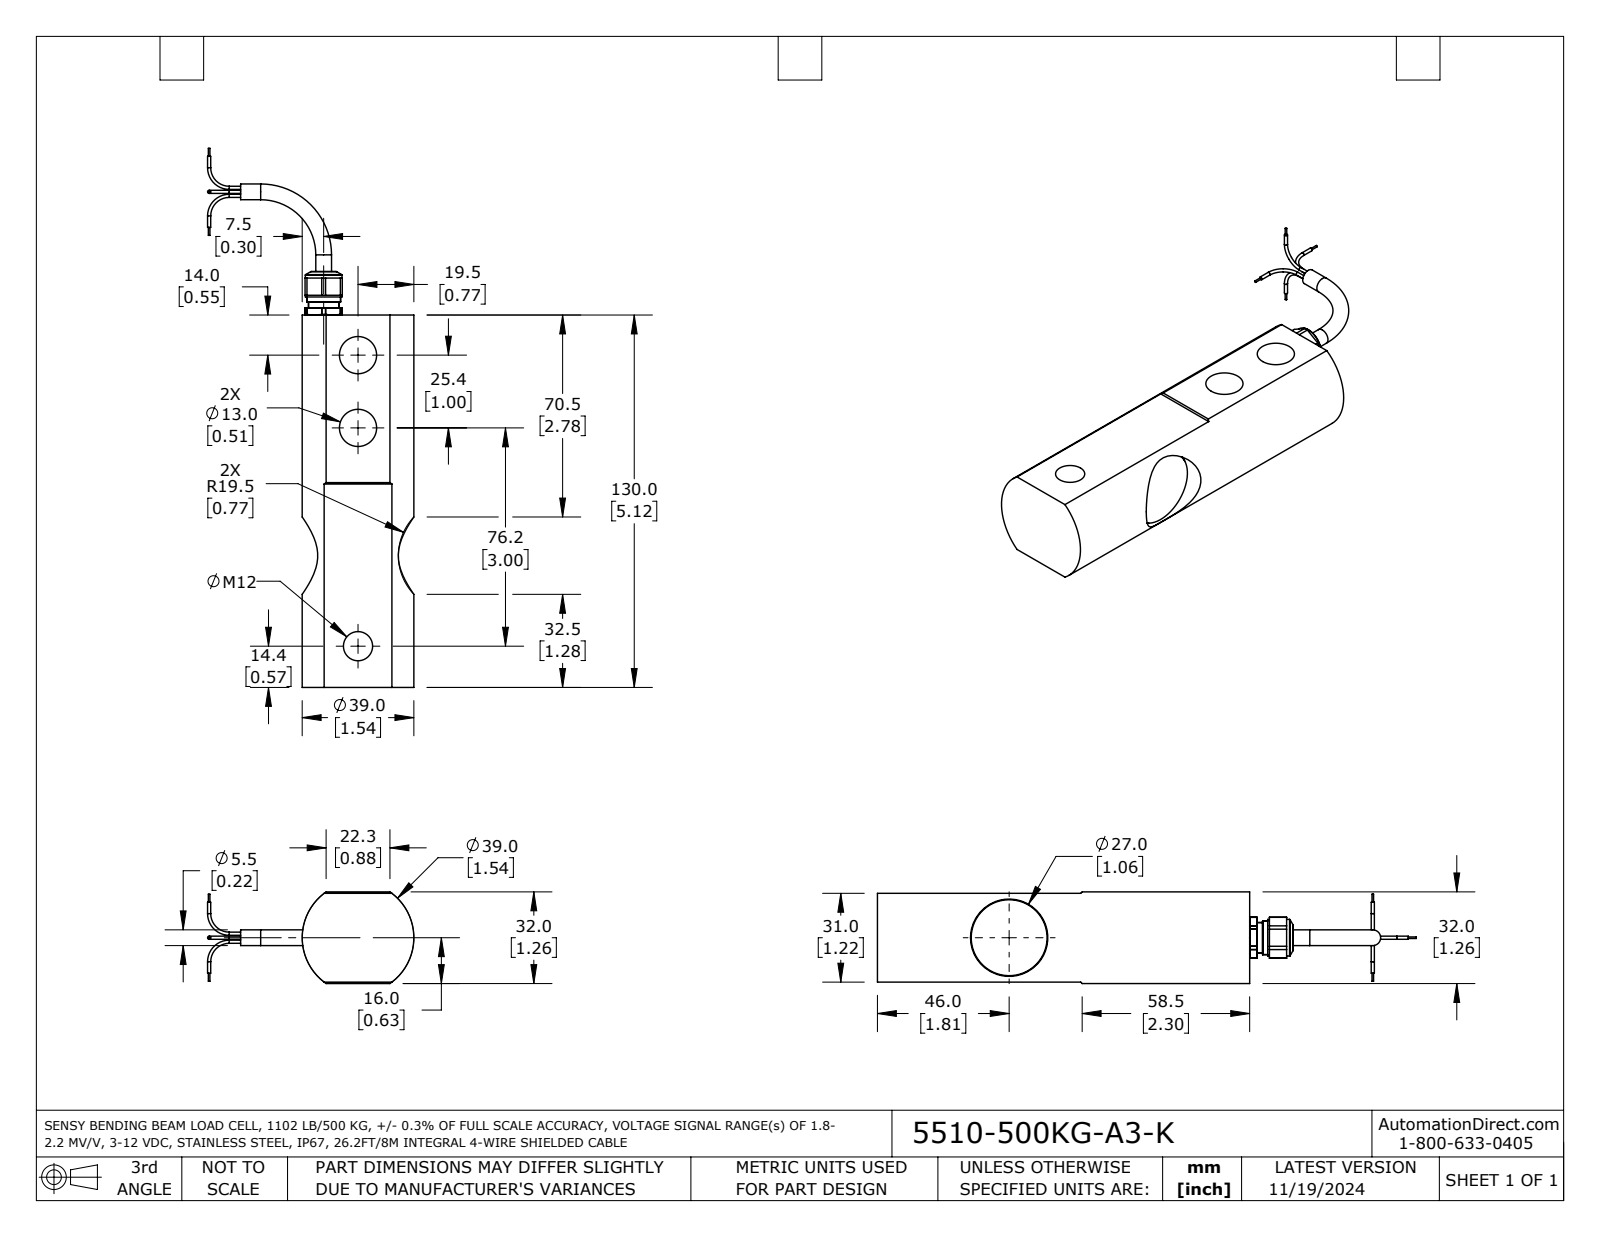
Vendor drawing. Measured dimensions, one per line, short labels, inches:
name: 5510-500KG-A3-K
written by: SolidWorks 2021 (AUTOMOTIVE_DESIGN)
unit: in
bodies: 11 solids, 247 faces (67 planar, 112 cylindrical, 68 other)
size: 7.409 × 2.837 × 1.26
volume: 7.667 in³; area: 42.32 in²
holes: 2× ⌀0.512, 1× ⌀0.126, 1× ⌀0.157, 1× ⌀0.173, 1× ⌀0.24, 1× ⌀0.244, 1× ⌀0.329, 1× ⌀0.354, 1× ⌀0.402, 1× ⌀0.439, 1× ⌀1.063
bosses: 6× ⌀0.043, 2× ⌀0.217, 2× ⌀0.022, 1× ⌀1.043, 1× ⌀0.504, 1× ⌀0.464, 1× ⌀0.433, 1× ⌀0.417
rounds: 1× R0.281, 1× R0.768
face distances: 0.02, 1.24, 1.22, 5.118, 1.26, 1.029, 0.197, 0.512, 0.531, 5.65
hole spacings: 1, 3, 4
